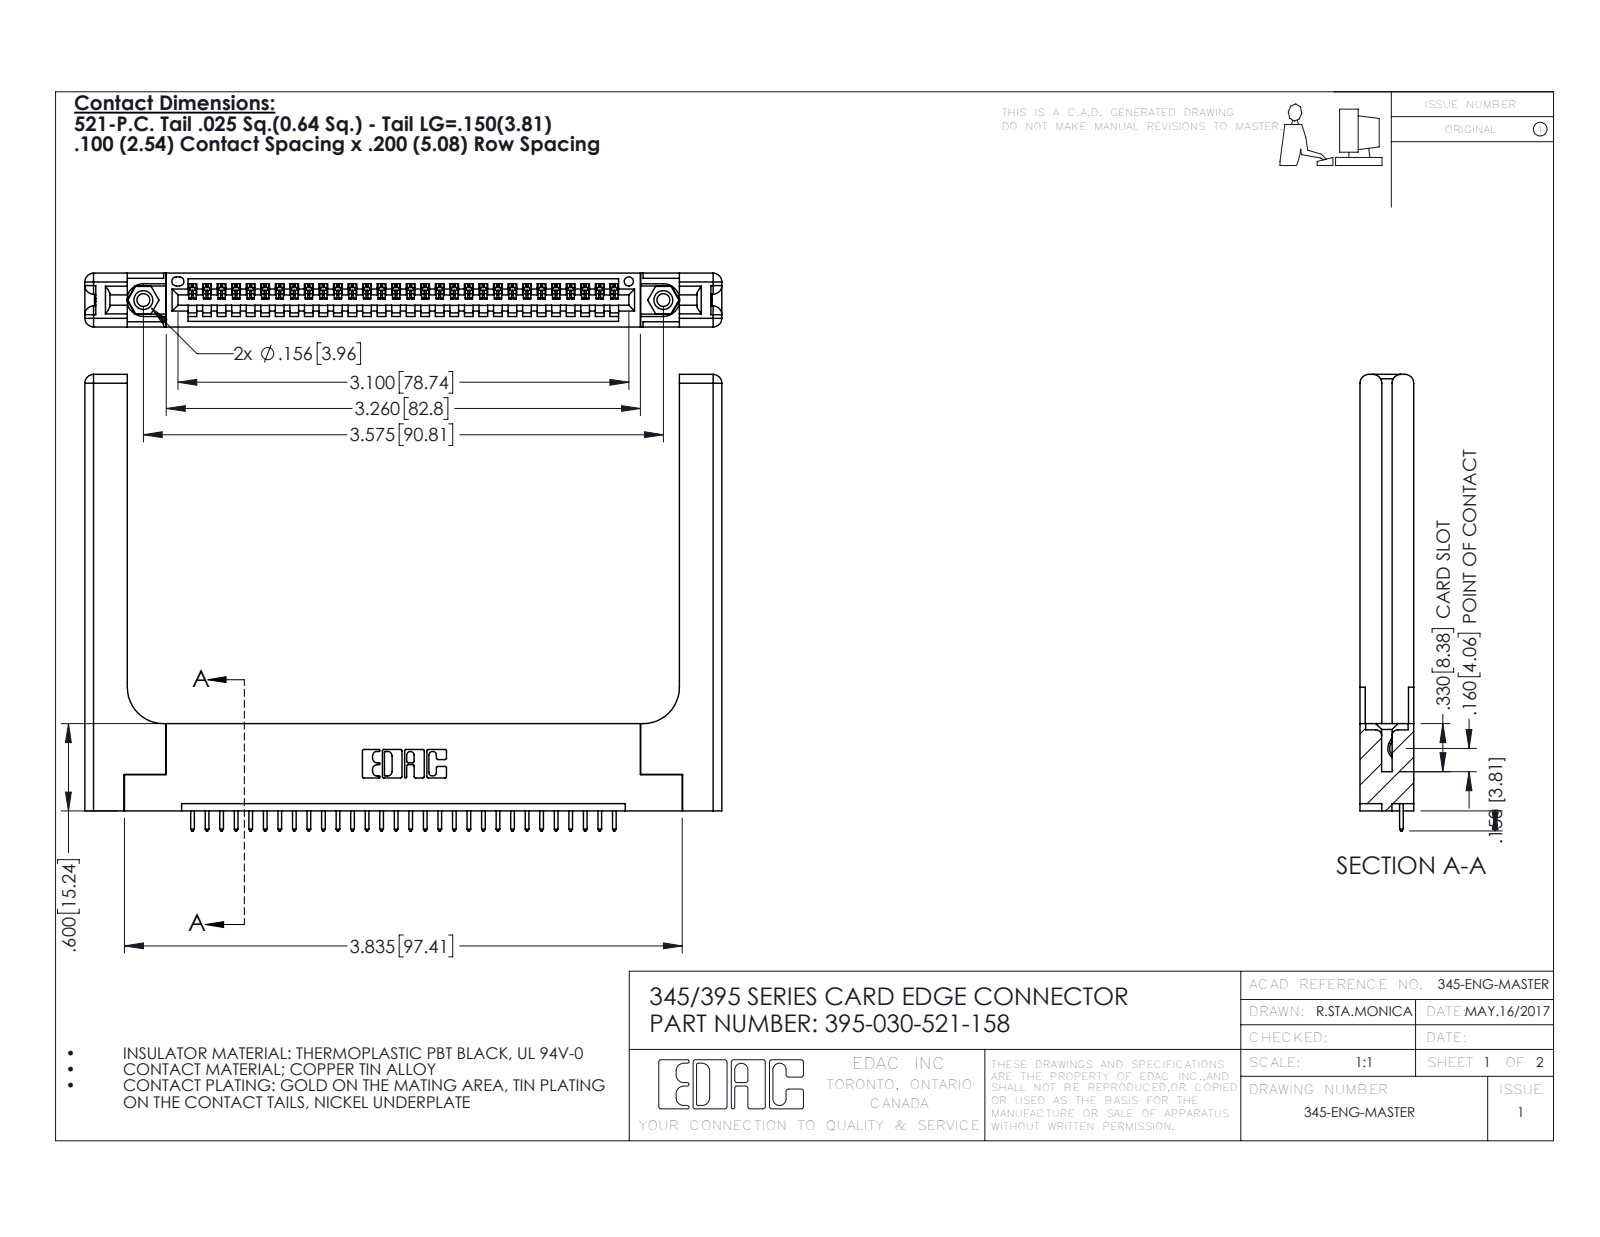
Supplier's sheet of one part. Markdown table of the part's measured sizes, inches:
| quantity | value |
| --- | --- |
| part name | 345-220-058_345-220-058; 395-030-521-158; 345 Part_Flush Mounting Lugs - 0.156 Dia-TH; 345-250-001_345-250-001-102 (+1 more) |
| STEP written by | SolidWorks 2016 (CONFIG_CONTROL_DESIGN) |
| units | inches |
| bodies | 35 solids, 2122 faces (1428 planar, 634 cylindrical, 60 other) |
| overall size | 4.379 × 3.137 × 0.37 |
| volume | 1.152 in³ |
| surface area | 28.84 in² |
| round holes (diameter × count) | 0.089 × 2, 0.125 × 2, 0.156 × 2, 0.064 × 1 |
| round bosses / shafts (diameter × count) | 0.155 × 2 |
| partial cylindrical surfaces (radius × count) | 0.006 × 60, 0.01 × 60, 0.01 × 22, 0.06 × 16, 0.007 × 6, 0.031 × 6, 0.026 × 3, 0.03 × 2 |
| main face-to-face distances | 0.37, 0.072, 0.298, 0.2, 0.098, 0.272, 0.025, 0.148, 0.15, 0.077 |
| hole center spacings | 0.27, 3.34, 3.575 |
